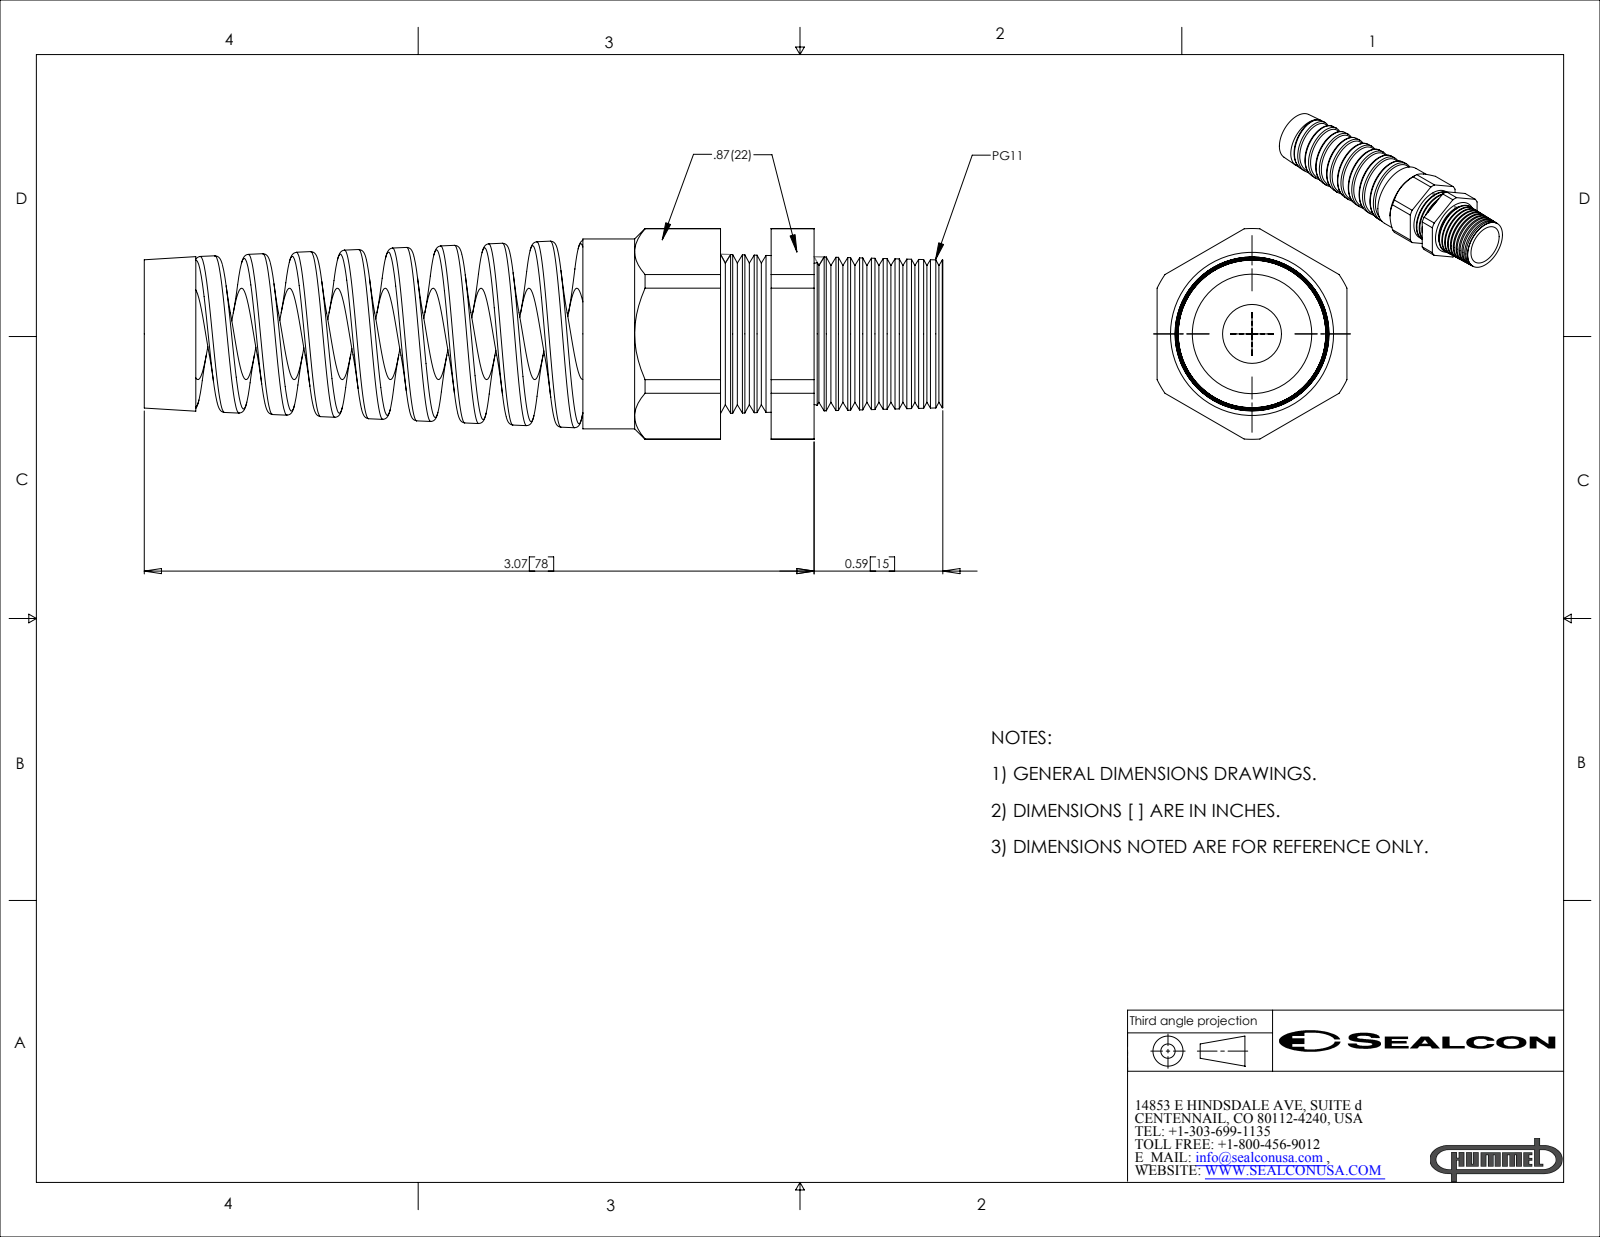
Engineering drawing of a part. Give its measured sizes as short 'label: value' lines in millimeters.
name: CF11CR-GY
written by: SolidWorks 2007 (CONFIG_CONTROL_DESIGN)
unit: mm
bodies: 2 solids, 196 faces (24 planar, 42 cylindrical, 130 other)
size: 93 × 24.5 × 22.1
volume: 16 670 mm³; area: 12 480 mm²
holes: 1× ⌀6.9, 1× ⌀10.6, 1× ⌀11.4
bosses: 1× ⌀22.1, 1× ⌀13.9
rounds: 1× R12.3
face distances: 22.1, 15.9, 10, 5.9, 6, 16, 21.9, 26.9, 20.9, 10.9
